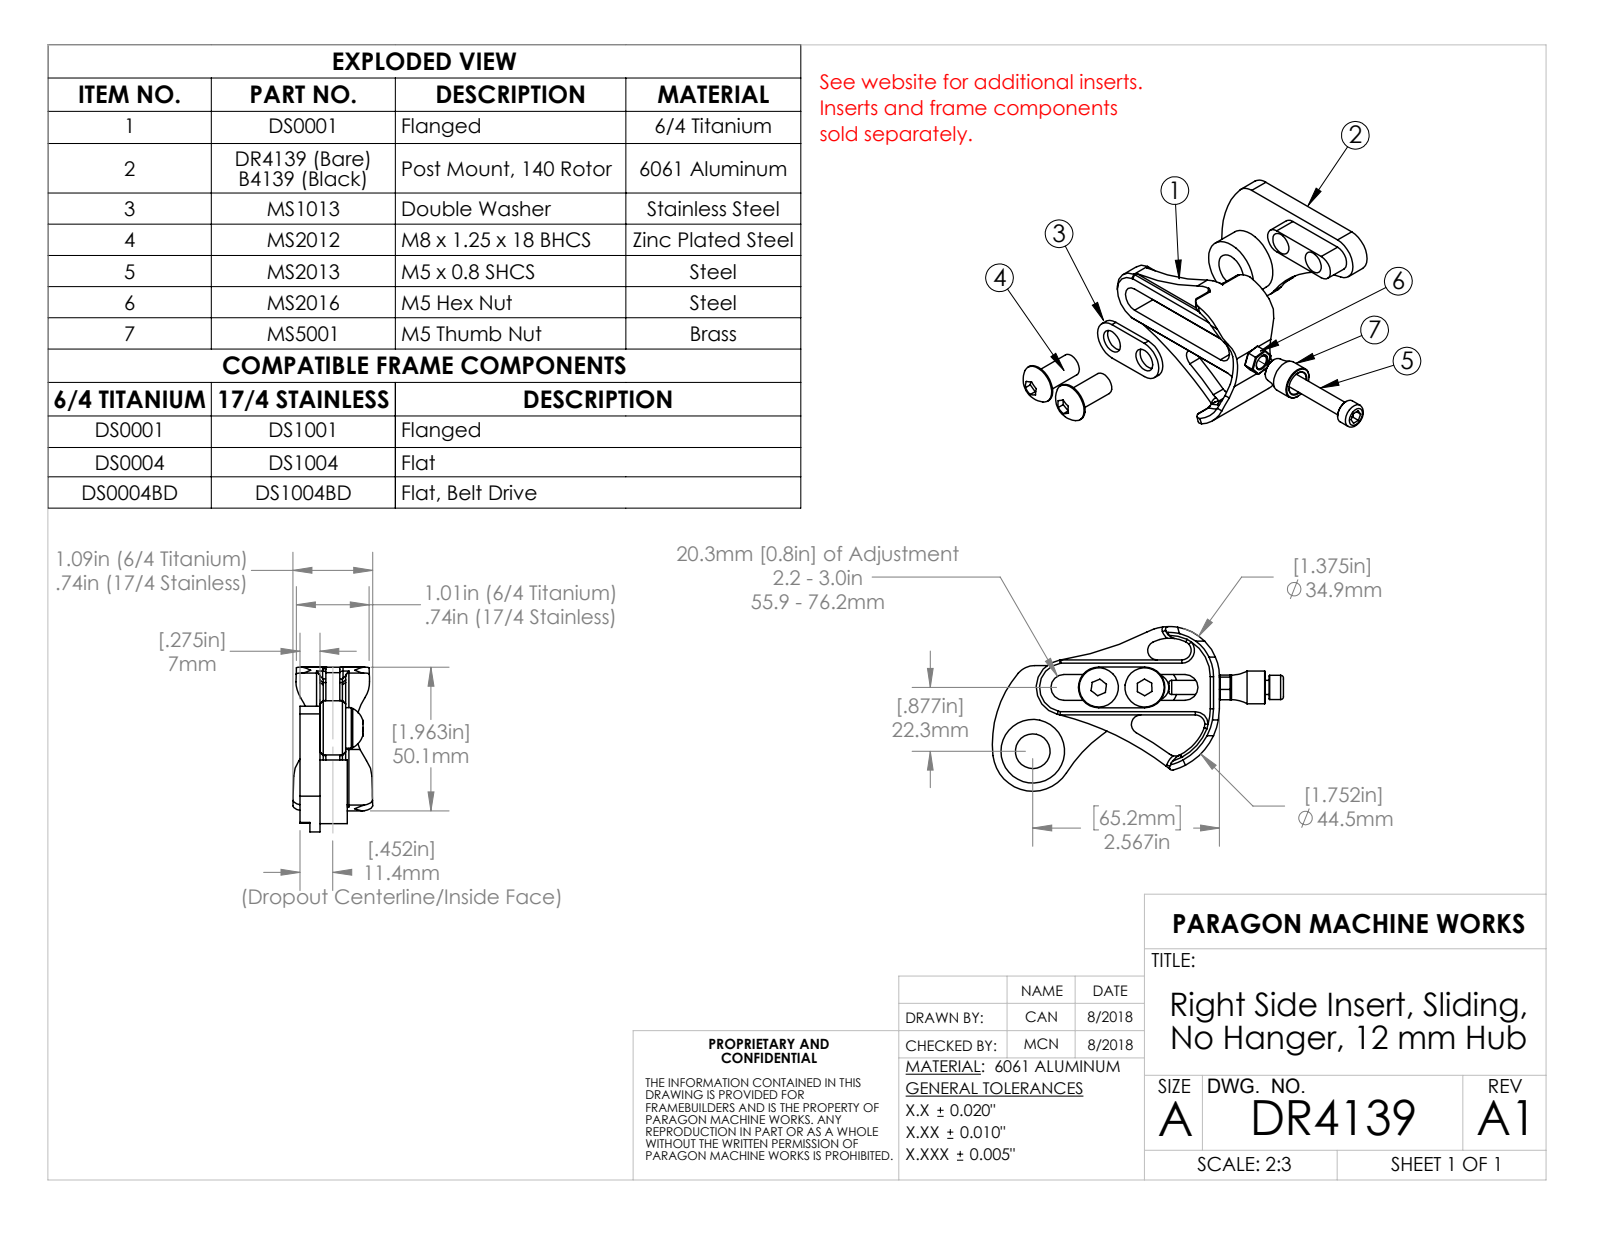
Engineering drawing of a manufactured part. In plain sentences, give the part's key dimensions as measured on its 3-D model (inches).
The part is named "DR4139". Its 3-D file was written by "SolidWorks 2023 (AUTOMOTIVE_DESIGN)". It is 1 solid with 33 faces: 10 planar, 23 cylindrical and 0 other. Overall it measures 2.358 by 2.082 by 0.65 inches. Its volume is 0.847 cubic inches and its surface area 10.78 square inches. Round holes: 2 of diameter 0.312, 1 of diameter 0.477. Round bosses or shafts: 1 of diameter 0.875. Partial cylindrical surfaces (rounded edges, fillets, slot ends): 2 of radius 0.039, 2 of radius 0.178, 2 of radius 0.3, 1 of radius 0.394, 1 of radius 0.5, 1 of radius 0.55, 1 of radius 1.5, 1 of radius 2. The main face-to-face distances are 0.275, 0.138, 0.137, 0.65, 0.512, 0.375, 0.478, 0.356, 0.122, 0.59. The hole center spacings are 0.63, 1.262, 1.77.
